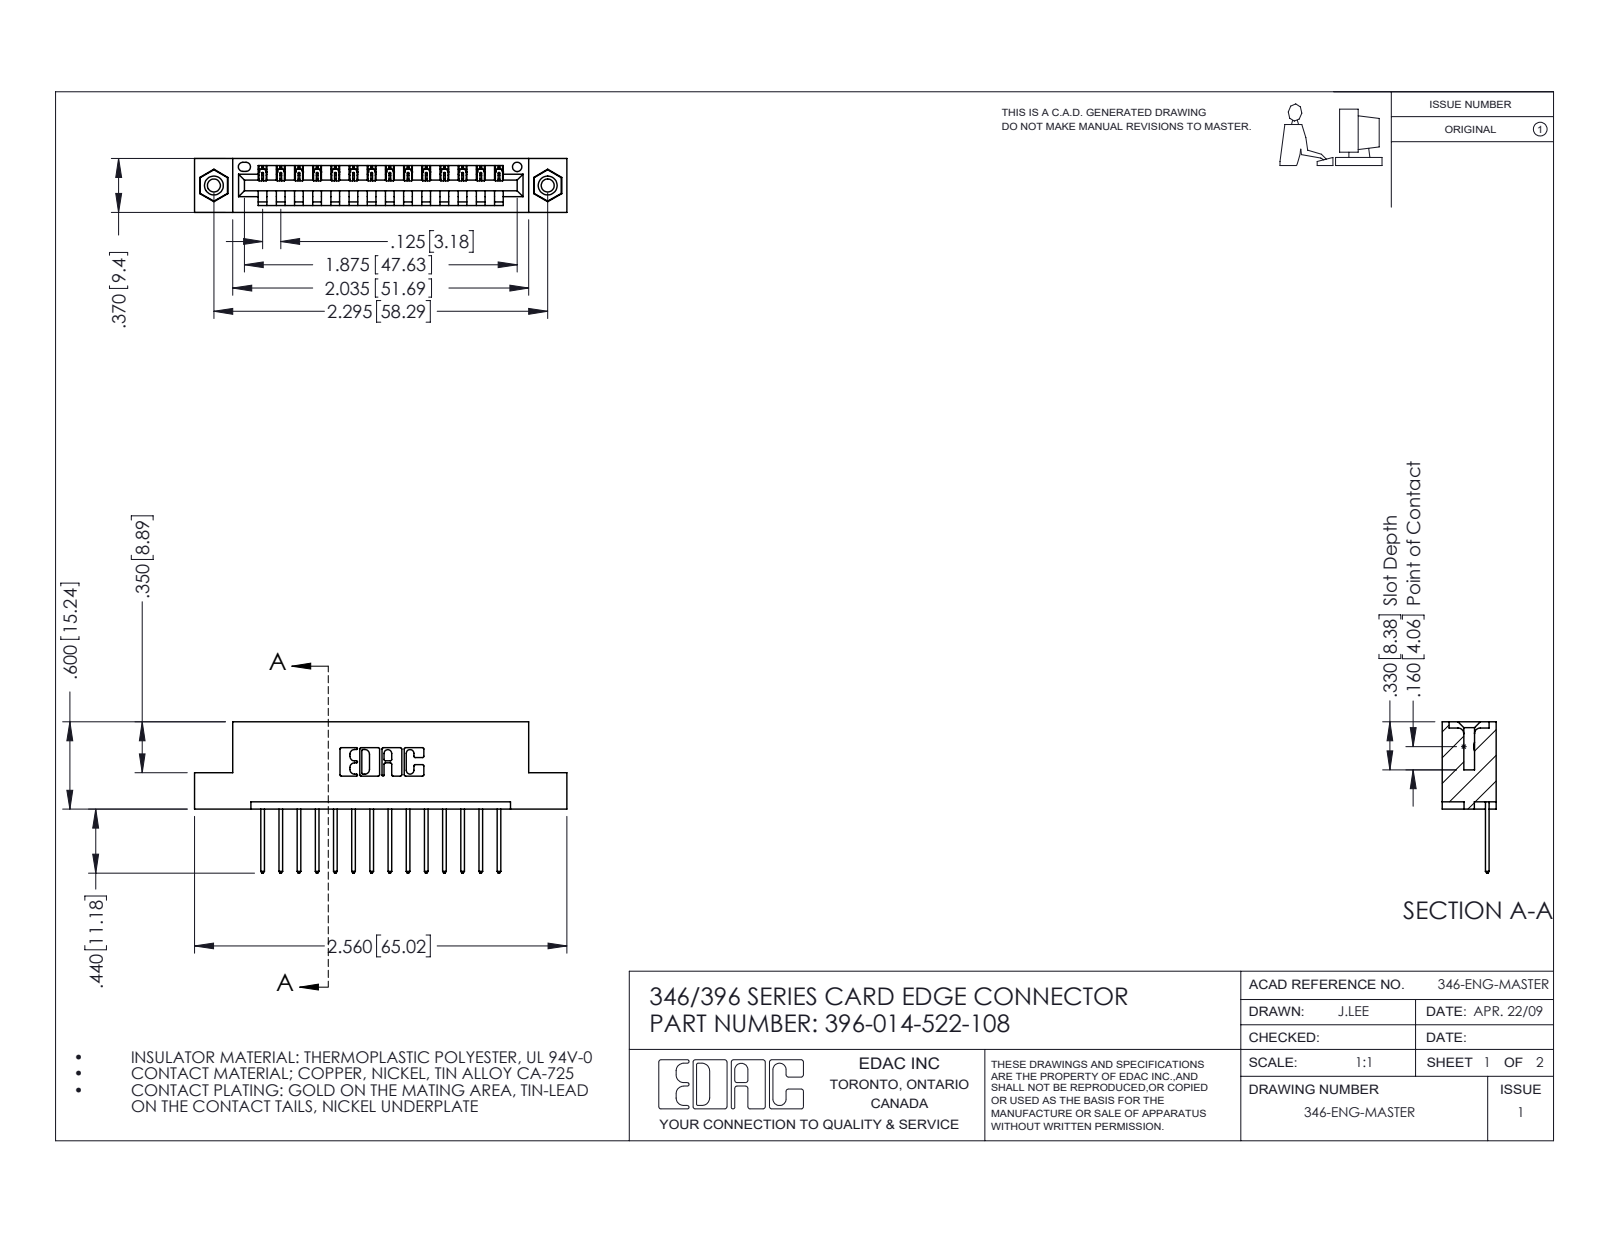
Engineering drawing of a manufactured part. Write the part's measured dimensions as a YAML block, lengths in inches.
part_name: "346 Part_Flush Mounting Lugs - 0.156 Dia-TI; 345-292-001_345-293-122; 396-014-522-108; 345-250-001_345-250-003-102"
step_written_by: "SolidWorks 2016 (CONFIG_CONTROL_DESIGN)"
units: inches
bodies: {solids: 17, faces: 994, planar: 668, cylindrical: 310, other: 16}
overall_size: [2.56, 1.04, 0.37]
volume: 0.368
surface_area: 11.32
round_holes:
  - {diameter: 0.089, count: 2}
  - {diameter: 0.125, count: 2}
  - {diameter: 0.156, count: 2}
  - {diameter: 0.064, count: 1}
round_bosses_or_shafts:
  - {diameter: 0.155, count: 2}
partial_cylinders:
  - {radius: 0.006, count: 28}
  - {radius: 0.01, count: 28}
  - {radius: 0.01, count: 22}
  - {radius: 0.007, count: 6}
  - {radius: 0.031, count: 6}
  - {radius: 0.026, count: 3}
  - {radius: 0.031, count: 2}
  - {radius: 0.04, count: 2}
face_to_face_distances: [0.25, 0.048, 0.322, 0.37, 0.072, 0.298, 0.025, 0.148, 0.222, 0.1]
hole_center_spacings: [0.246, 2.089, 2.295]
